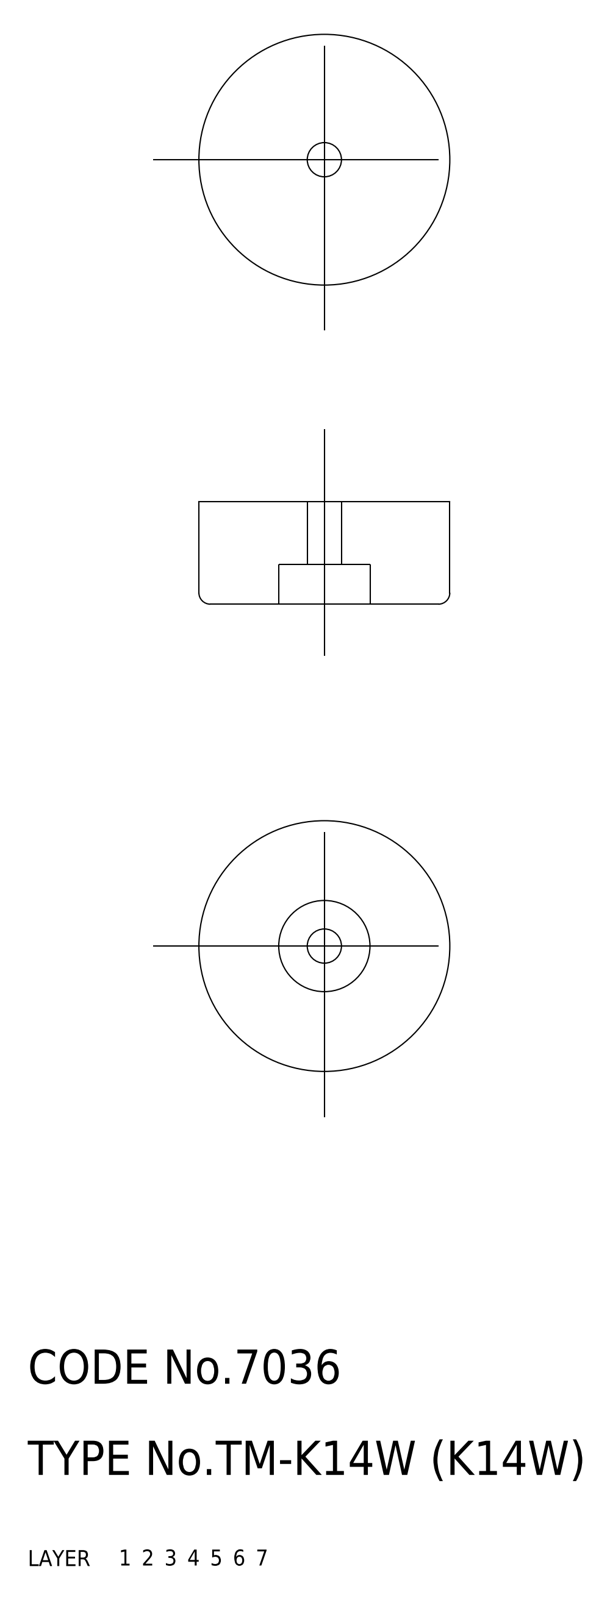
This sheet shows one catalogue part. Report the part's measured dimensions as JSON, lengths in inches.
{"part_name": "washer; rubber foot; K14W_5950_36", "step_written_by": "CADfix (AUTOMOTIVE_DESIGN)", "units": "inches", "bodies": {"solids": 2, "faces": 23, "planar": 0, "cylindrical": 0, "other": 23}, "overall_size": [0.866, 0.866, 0.354], "volume_in3": 0.195, "surface_area_in2": 2.678}
